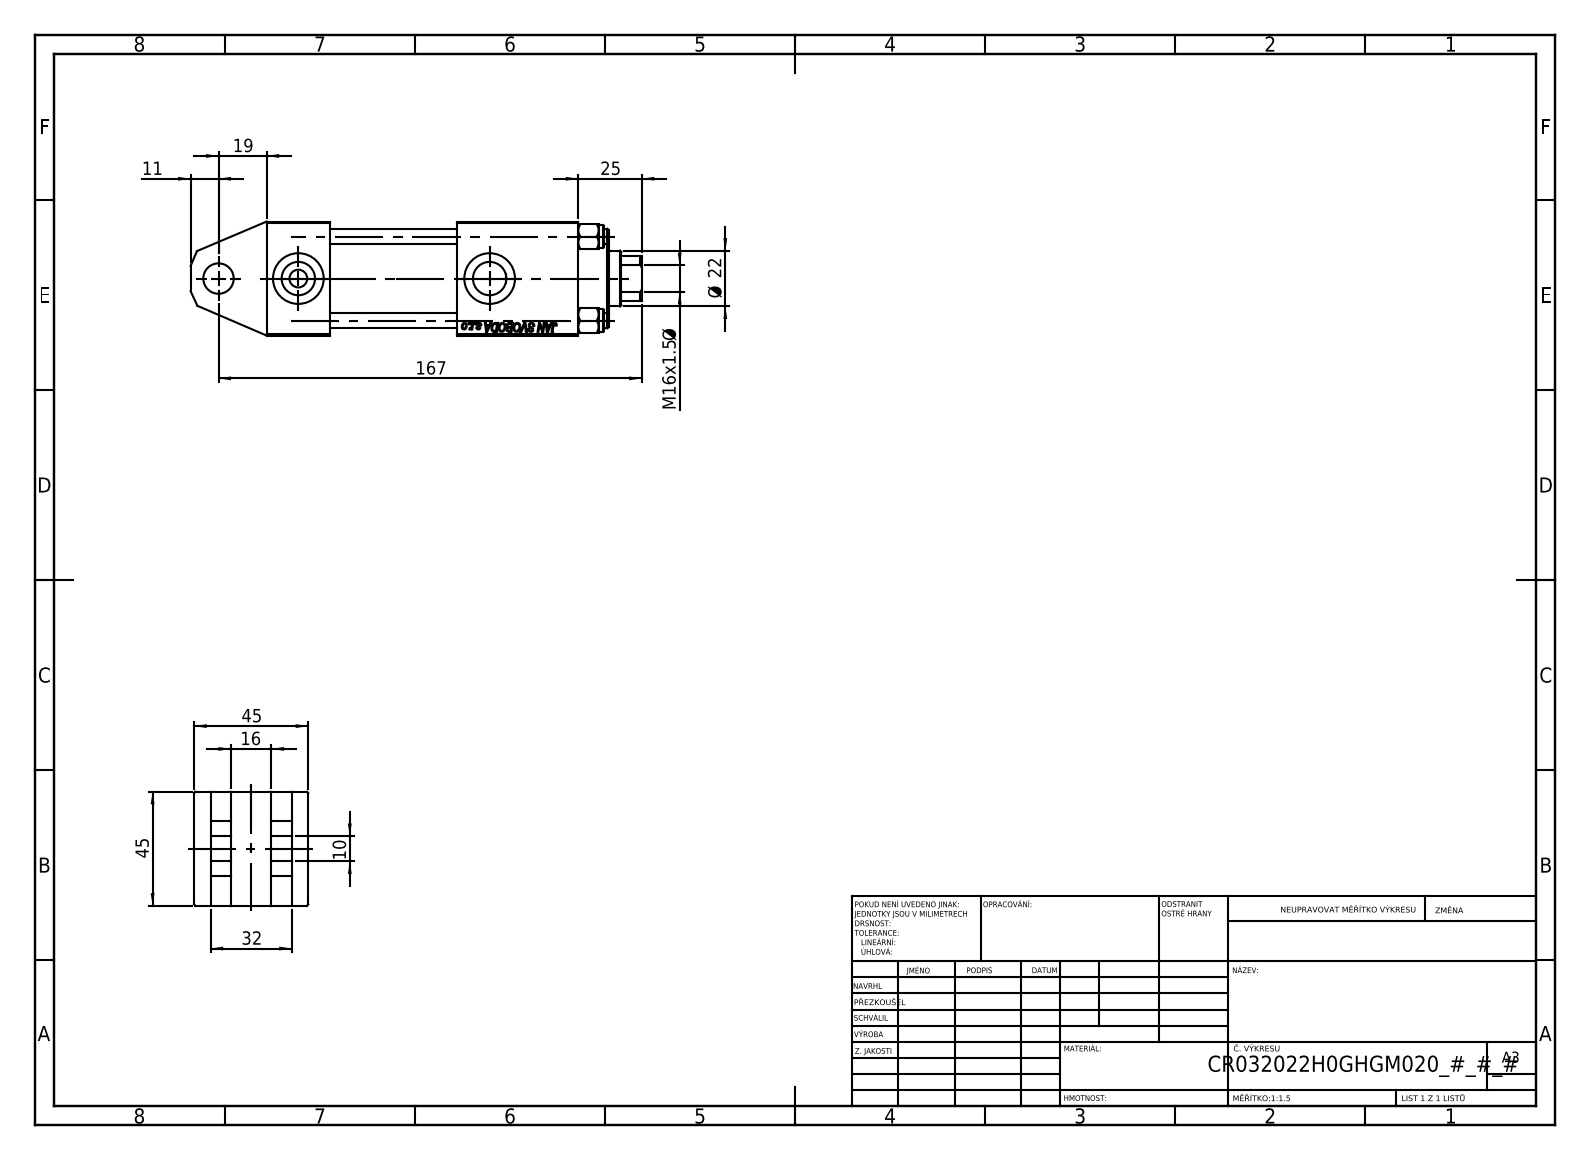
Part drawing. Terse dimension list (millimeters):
name: V215CR_H_Body; NUT_M5_H; V215CR_TYCINKA_H; V215_VC_A (+1 more)
written by: SolidWorks 2019 (CONFIG_CONTROL_DESIGN)
unit: mm
bodies: 11 solids, 1128 faces (517 planar, 83 cylindrical, 528 other)
size: 178 × 45 × 45
volume: 225 167 mm³; area: 78 357 mm²
holes: 4× ⌀6, 2× ⌀7, 2× ⌀13.16, 2× ⌀20, 1× ⌀10.5, 1× ⌀12, 1× ⌀22, 1× ⌀24, 1× ⌀25, 1× ⌀32, 1× ⌀33
bosses: 4× ⌀9, 1× ⌀38, 1× ⌀34
rounds: 1× R10.5
face distances: 45, 8, 38.5, 6.5, 14.5, 30.5, 24, 25, 123, 50
hole spacings: 23.48, 33.2, 46.95, 31.5, 75.5, 107
